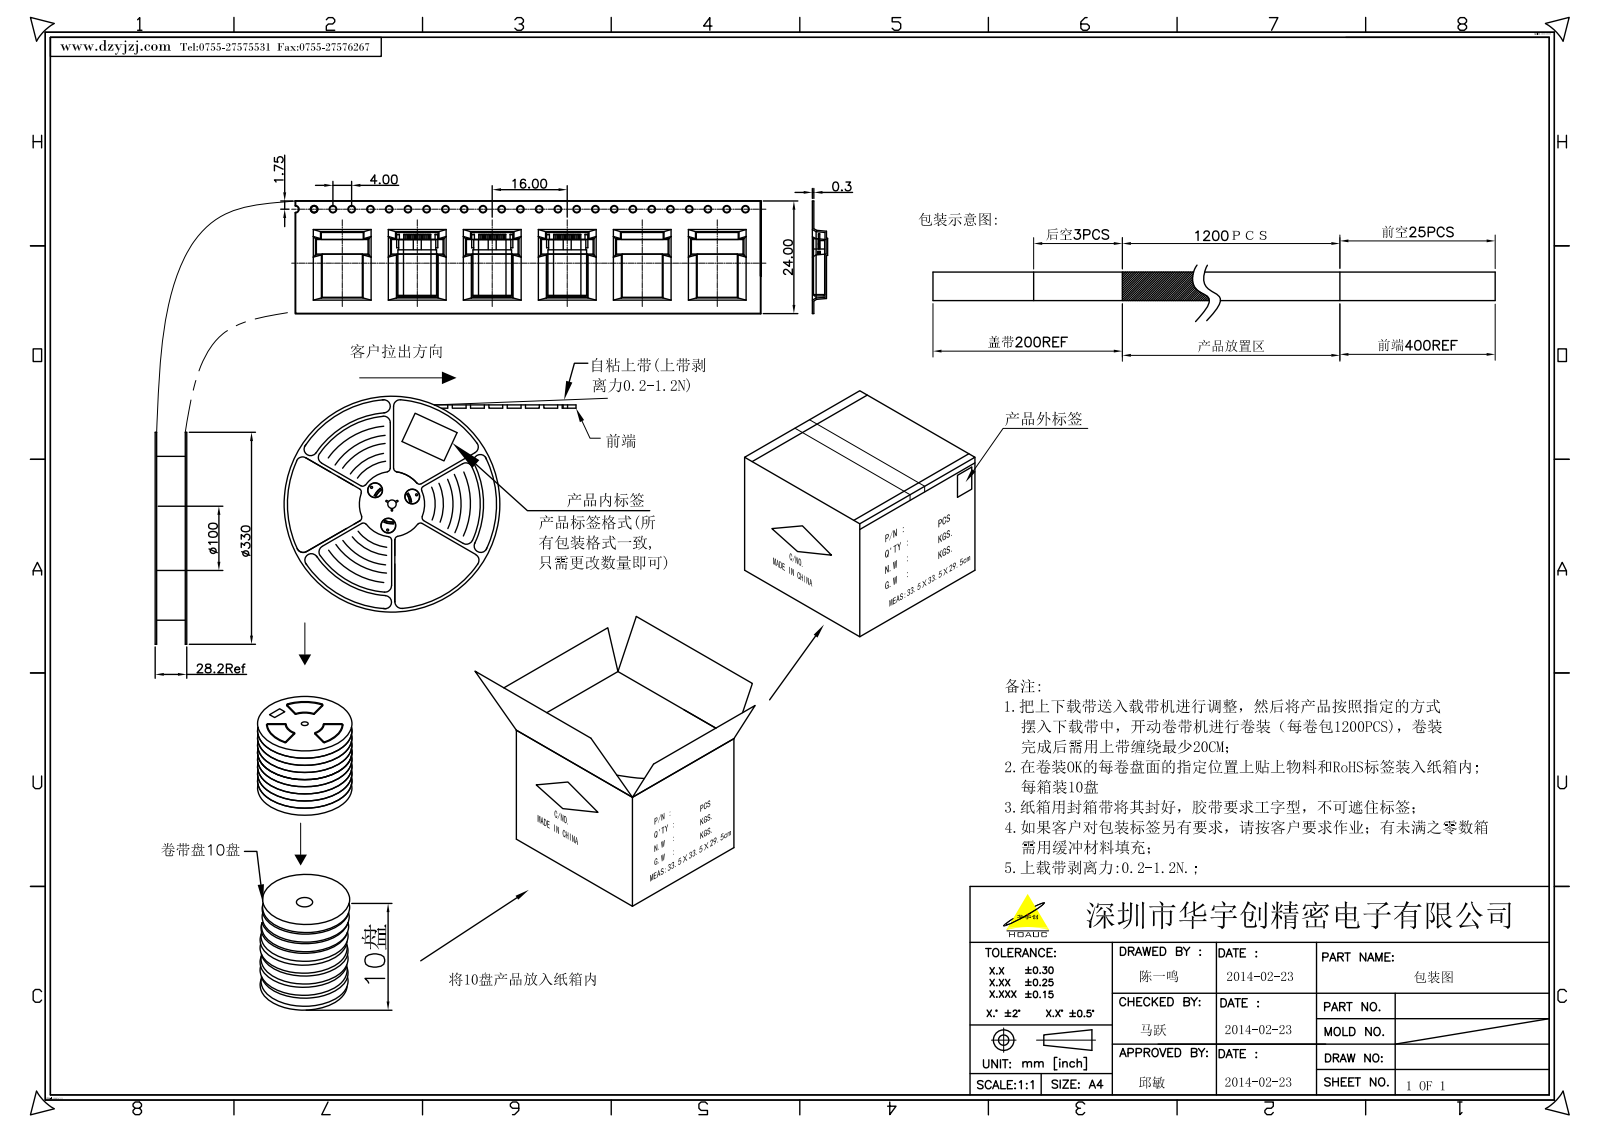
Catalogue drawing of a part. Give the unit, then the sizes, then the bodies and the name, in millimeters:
Units: millimetres
Overall size (bounding box): 13.3 × 8.8 × 2.4
Round holes (diameter × count): ⌀0.5 ×2
Partial cylindrical surfaces — rounded edges, fillets, slot ends (radius × count): R0.3 ×8, R0.1 ×6, R0.25 ×6, R0.15 ×4, R1.05 ×4, R0.58 ×2, R0.6 ×2, R0.9 ×2
Main face-to-face distances: 0.8, 2.4, 1.6, 1.05, 0.55, 1.35, 1.85, 0.5, 1.04, 0.56
Hole centre spacings: 4.6
Volume: 180 mm³ · Surface area: 419 mm²
Bodies: 1 solid, 411 faces (329 planar, 76 cylindrical, 6 other)
Part name (STEP PRODUCT): XDS-A_TC_2_M_215I_ASM
STEP written by: CREO PARAMETRIC BY PTC INC, 2022073 (AUTOMOTIVE_DESIGN)
